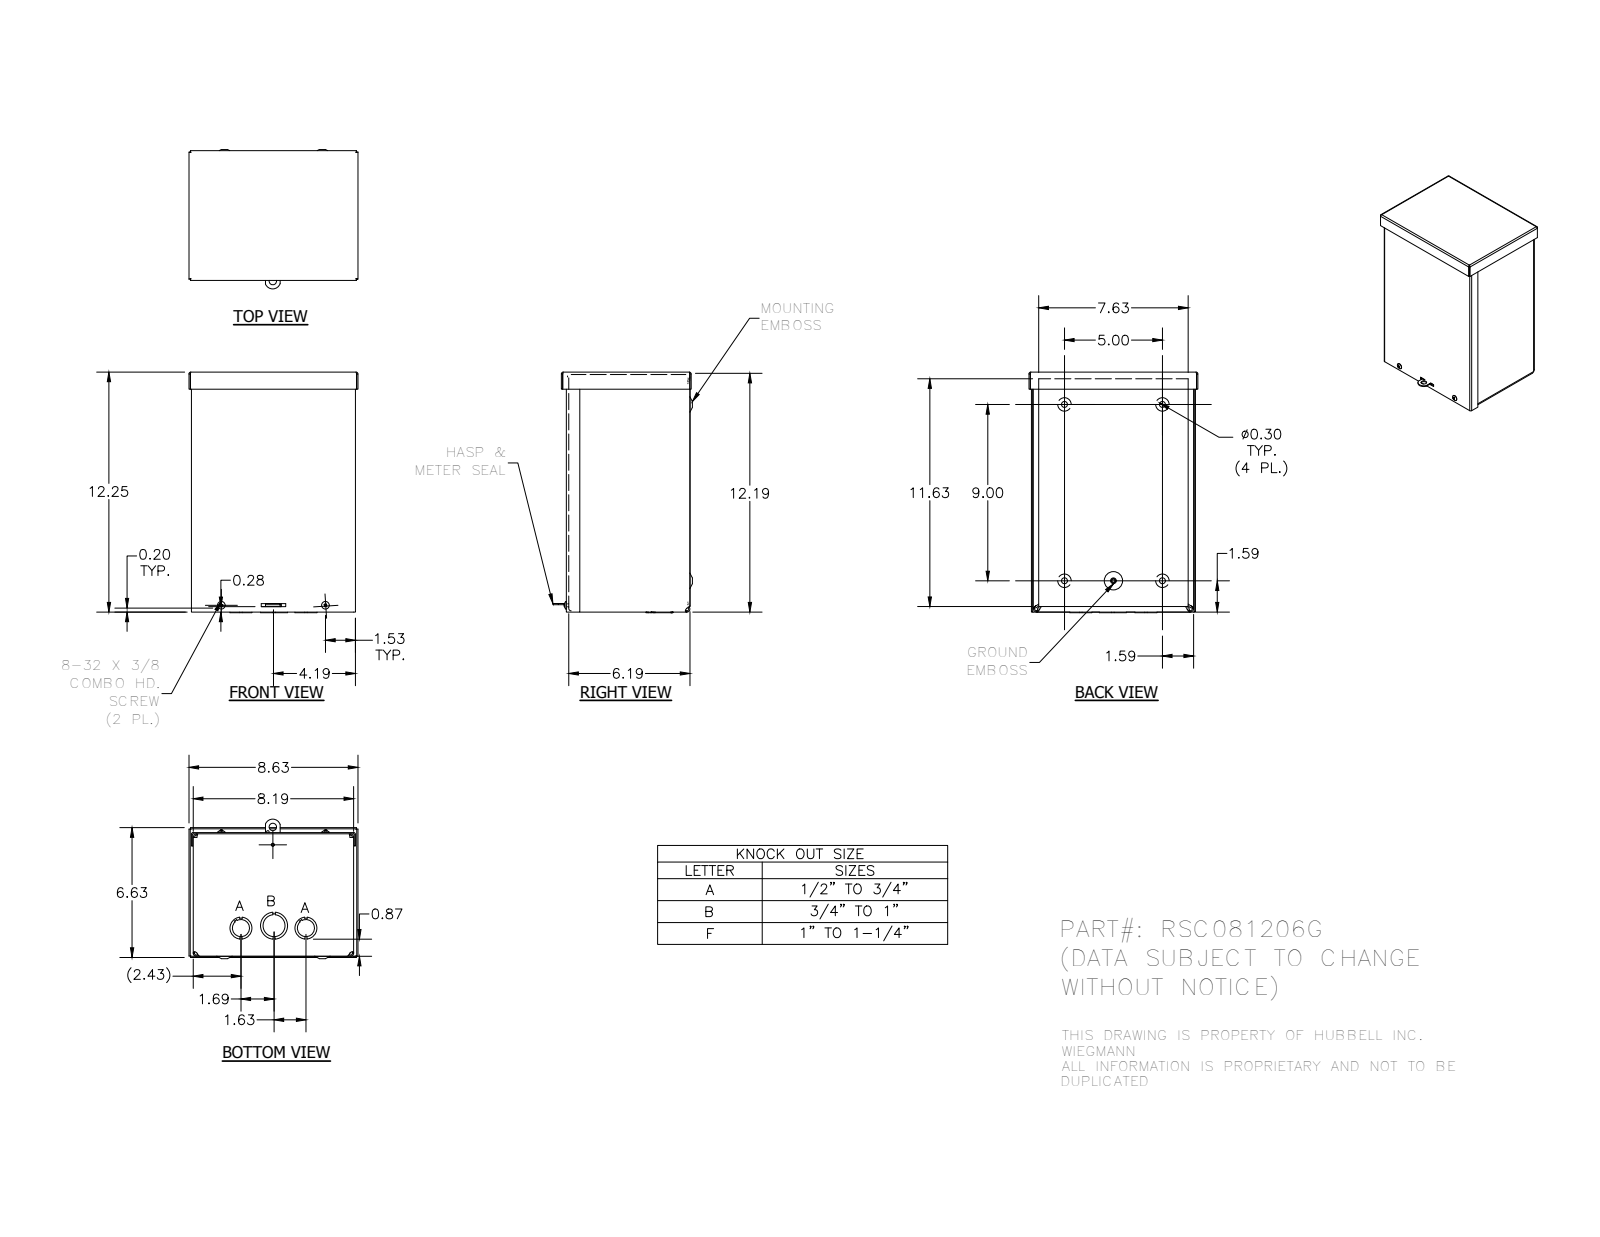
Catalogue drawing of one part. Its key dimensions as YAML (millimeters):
part_name: "RSC081206G_WRAP; RSC0812G_LID; RSC0806G_CAP; 3183 (+4 more)"
step_written_by: "Autodesk Inventor 2014 (AUTOMOTIVE_DESIGN)"
units: millimeters
bodies: {solids: 7, faces: 503, planar: 238, cylindrical: 121, other: 144}
overall_size: [311.93, 219.07, 180.97]
volume: 600332
surface_area: 772469
round_holes:
  - {diameter: 7.62, count: 4}
  - {diameter: 7.95, count: 4}
  - {diameter: 28.57, count: 3}
  - {diameter: 3.17, count: 2}
  - {diameter: 3.76, count: 2}
  - {diameter: 22.22, count: 2}
  - {diameter: 3.96, count: 1}
  - {diameter: 4.19, count: 1}
  - {diameter: 9.52, count: 1}
  - {diameter: 34.92, count: 1}
round_bosses_or_shafts:
  - {diameter: 9.75, count: 2}
  - {diameter: 4.17, count: 2}
  - {diameter: 5.8, count: 1}
partial_cylinders:
  - {radius: 0.25, count: 10}
  - {radius: 0.79, count: 8}
  - {radius: 2.37, count: 8}
  - {radius: 3.17, count: 8}
  - {radius: 4.75, count: 8}
  - {radius: 0.53, count: 4}
  - {radius: 0.79, count: 4}
  - {radius: 1.4, count: 4}
face_to_face_distances: [1.58, 206.39, 1.57, 158.73, 157.15, 1.59, 307.99, 160.32, 158.74, 3.15]
hole_center_spacings: [27.24, 32.03, 63.5, 127, 134.95, 228.6, 237.25, 255.58]
